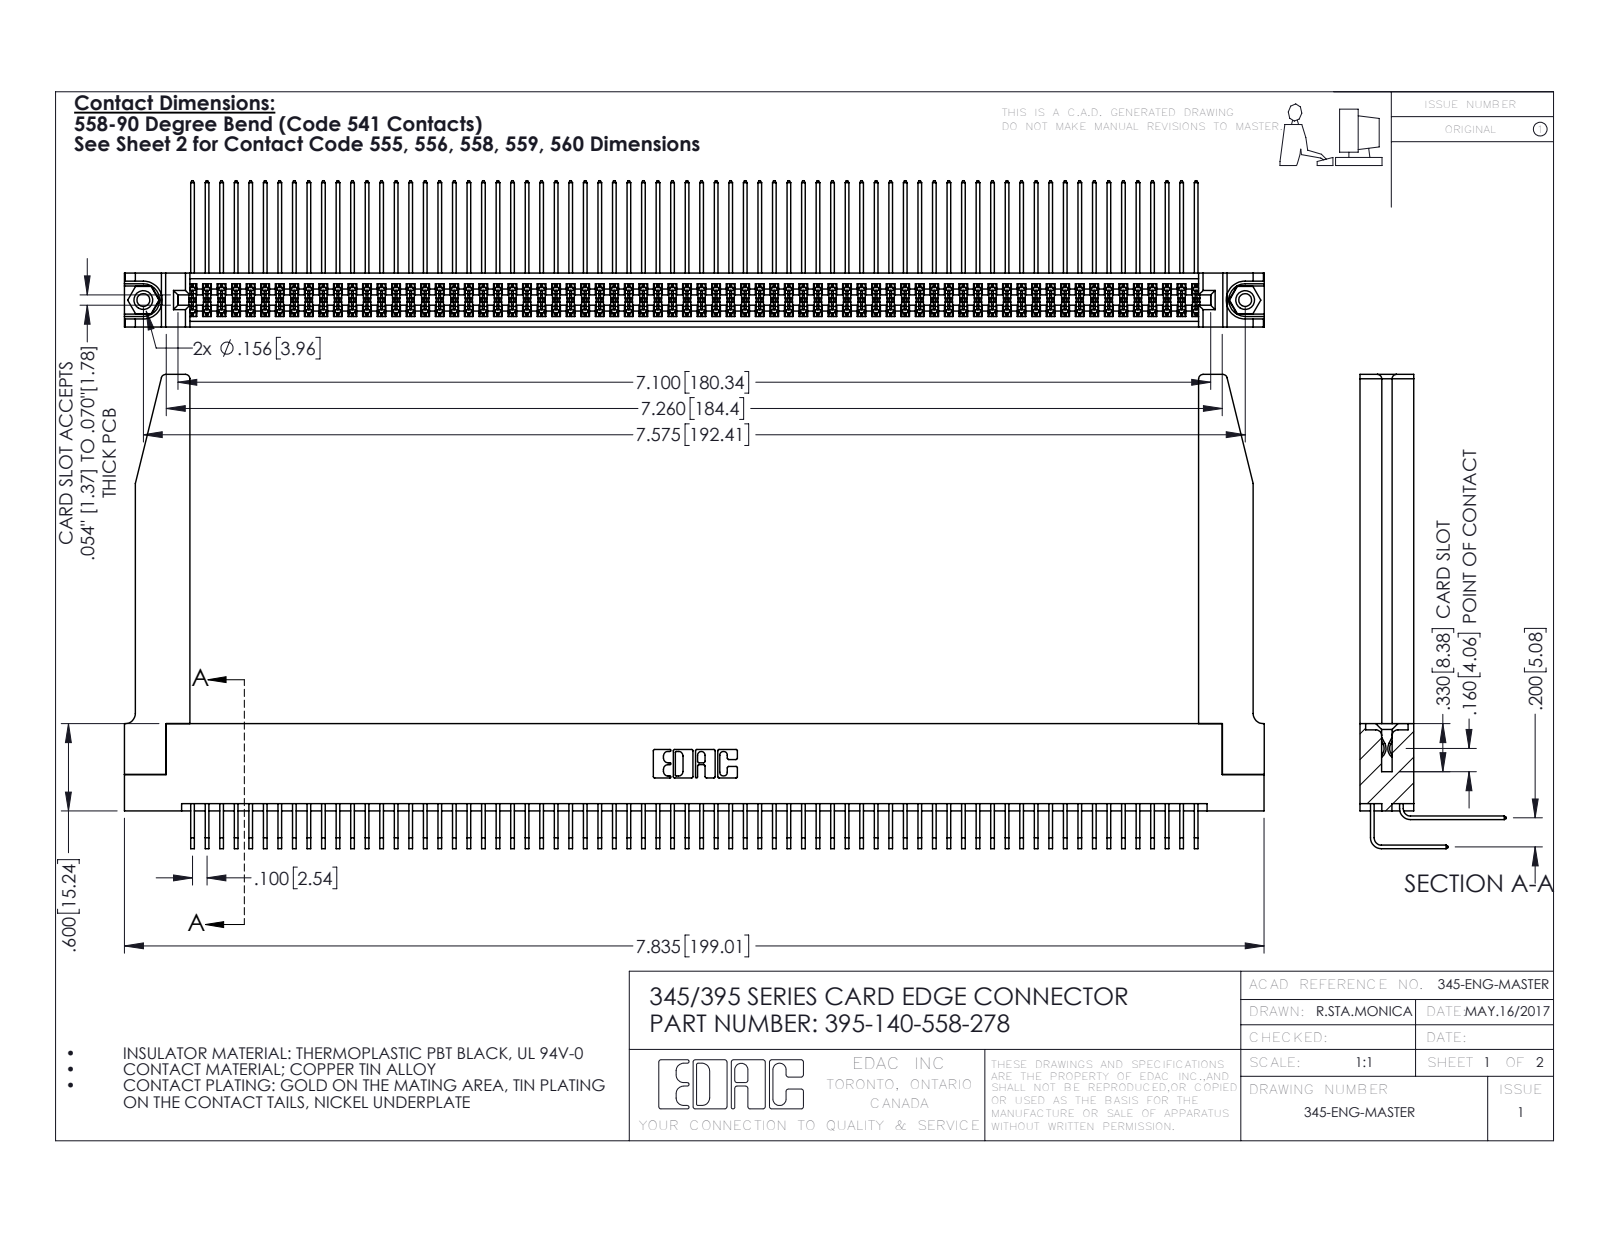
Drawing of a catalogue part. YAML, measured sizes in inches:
part_name: "345-292-001_558 Tail - 2; 395-140-558-278; 345 Part_Flush Mounting Lugs - 0.156 Dia-TH; 345-292-001_558 559 Tail - 1 (+2 more)"
step_written_by: "SolidWorks 2016 (CONFIG_CONTROL_DESIGN)"
units: inches
bodies: {solids: 145, faces: 7640, planar: 5122, cylindrical: 2466, other: 52}
overall_size: [7.836, 3.259, 1.005]
volume: 1.719
surface_area: 64.07
round_holes:
  - {diameter: 0.089, count: 2}
  - {diameter: 0.125, count: 2}
  - {diameter: 0.156, count: 2}
  - {diameter: 0.064, count: 1}
round_bosses_or_shafts:
  - {diameter: 0.155, count: 2}
partial_cylinders:
  - {radius: 0.006, count: 279}
  - {radius: 0.01, count: 22}
  - {radius: 0.03, count: 8}
  - {radius: 0.007, count: 6}
  - {radius: 0.031, count: 6}
  - {radius: 0.026, count: 3}
  - {radius: 0.014, count: 2}
  - {radius: 0.019, count: 2}
face_to_face_distances: [0.072, 0.298, 0.2, 0.37, 0.098, 0.272, 0.025, 0.225, 0.025, 0.175]
hole_center_spacings: [0.27, 7.339, 7.575]
